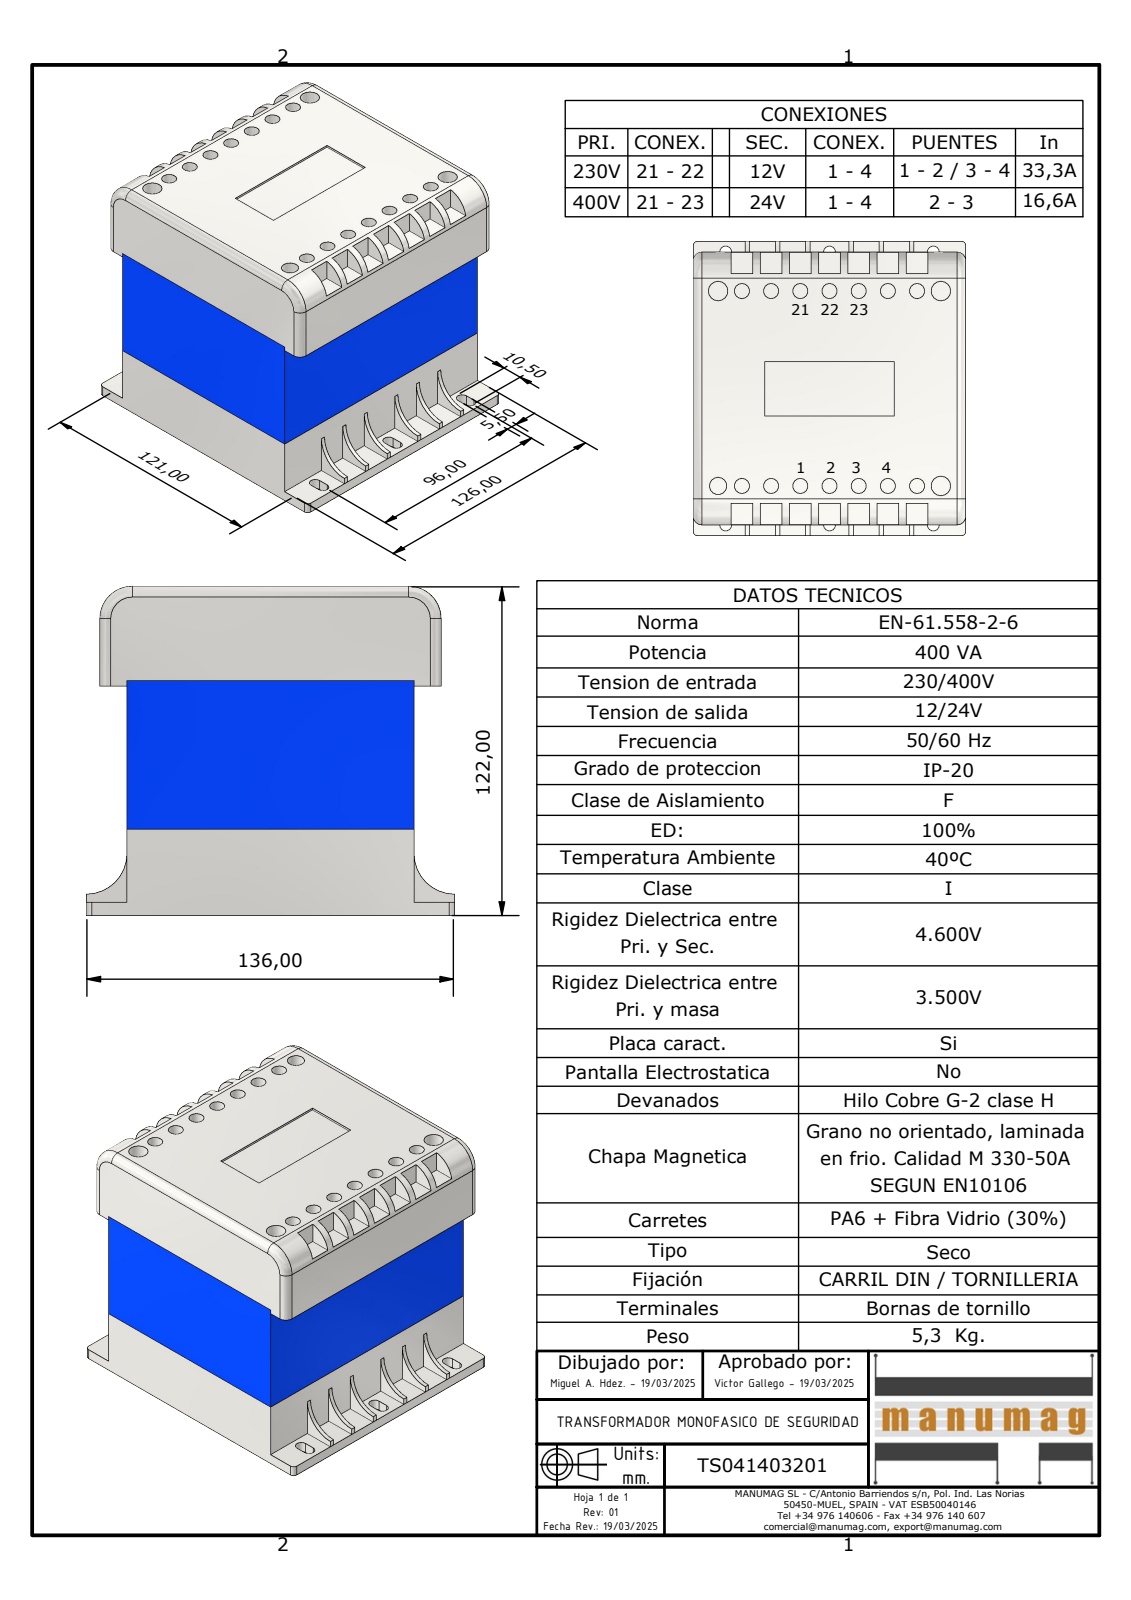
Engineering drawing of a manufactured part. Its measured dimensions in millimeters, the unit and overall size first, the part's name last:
Units: millimetres
Overall size (bounding box): 136 × 126 × 122
Round holes (diameter × count): ⌀7 ×14, ⌀9 ×3, ⌀8 ×1
Partial cylindrical surfaces — rounded edges, fillets, slot ends (radius × count): R2.75 ×12, R4 ×6, R2 ×4, R12 ×2, R15 ×2
Main face-to-face distances: 1, 105, 5, 125, 126, 87, 82, 106, 104, 122
Hole centre spacings: 13.5, 91.01, 27, 93.96, 90, 40.5, 98.69, 54
Volume: 656 709 mm³ · Surface area: 172 452 mm²
Bodies: 15 solids, 244 faces (186 planar, 54 cylindrical, 4 other)
Part name (STEP PRODUCT): TS041403201; INFERIOR EI120; CENTRAL EI120-50; SUPERIOR EI120
STEP written by: Autodesk Inventor 2023 (AUTOMOTIVE_DESIGN)
